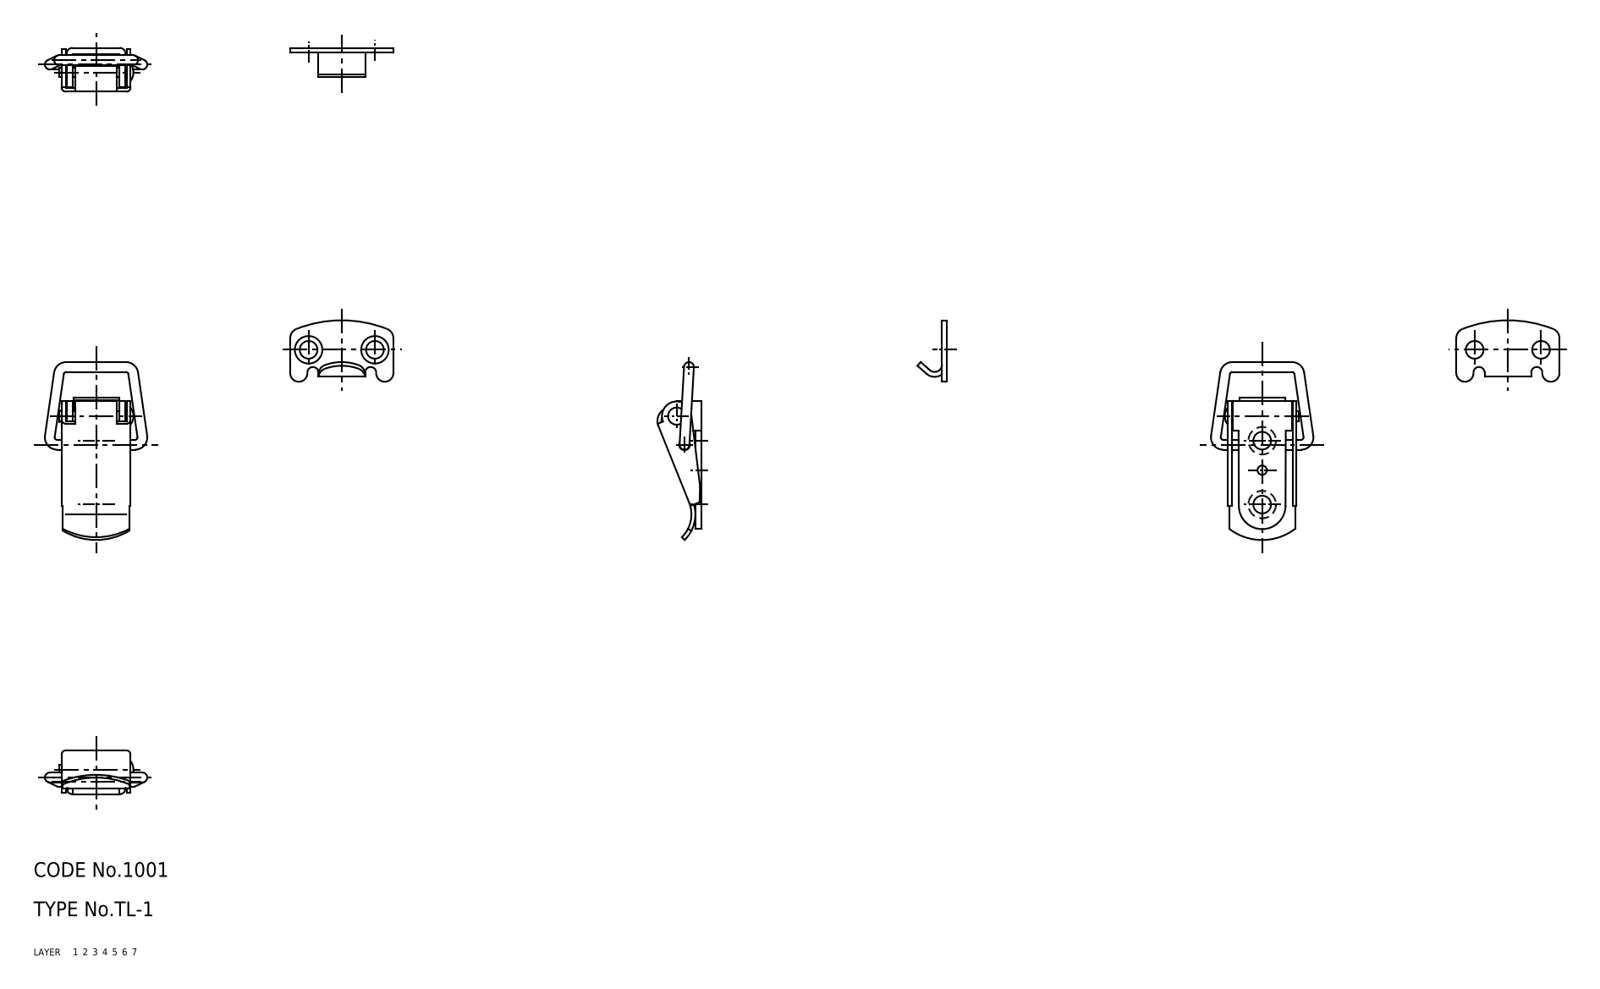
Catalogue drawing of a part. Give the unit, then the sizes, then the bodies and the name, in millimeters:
Units: millimetres
Overall size (bounding box): 44.71 × 21 × 8.91
Volume: 1 334 mm³ · Surface area: 3 365 mm²
Bodies: 6 solids, 139 faces (0 planar, 0 cylindrical, 139 other)
Part name (STEP PRODUCT): keeper; shaft; lever; leaf spring (+3 more)
STEP written by: CADfix (AUTOMOTIVE_DESIGN)
